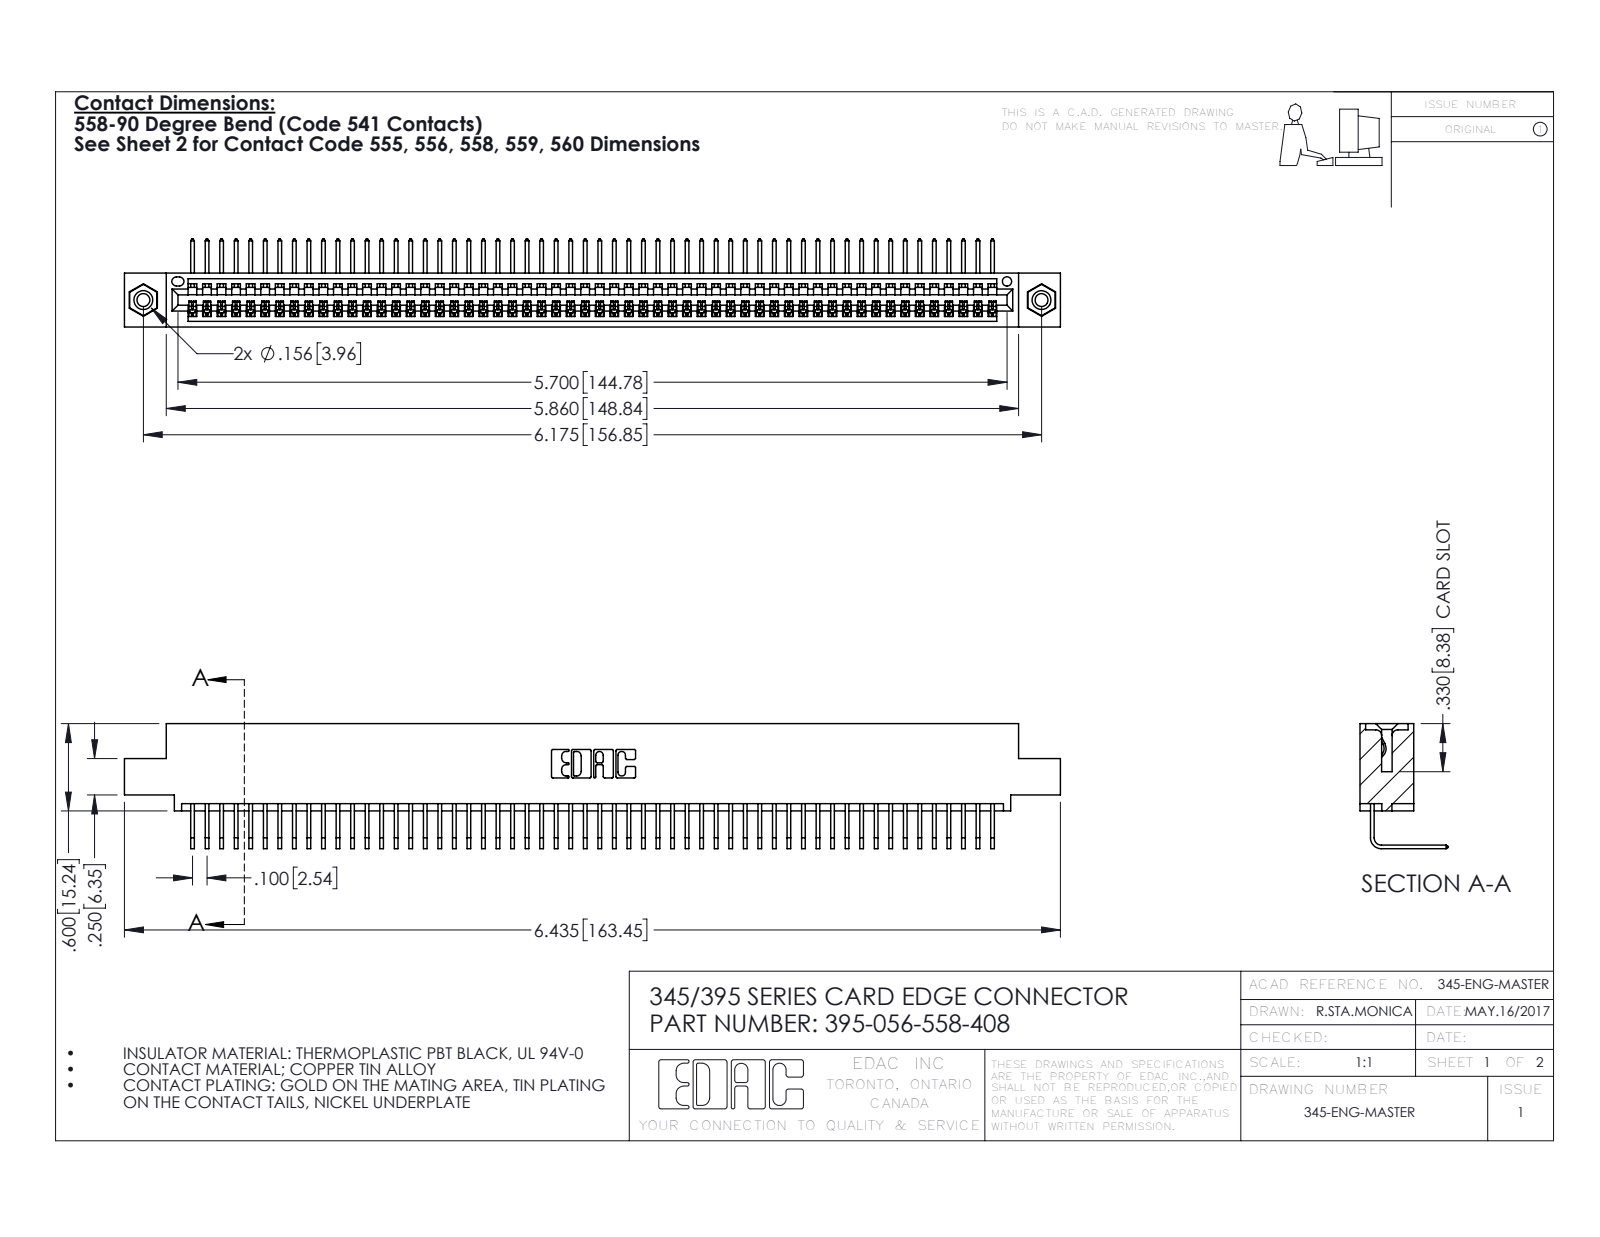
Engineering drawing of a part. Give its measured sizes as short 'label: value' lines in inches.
name: 345-292-001_558 Tail - 2; 345-250-001_345-250-003-102; 395-056-558-408; 345 Part_0.110 Offset - 0.156 Dia-TI
written by: SolidWorks 2016 (CONFIG_CONTROL_DESIGN)
unit: in
bodies: 59 solids, 3550 faces (2468 planar, 1066 cylindrical, 16 other)
size: 6.435 × 0.859 × 0.605
volume: 0.961 in³; area: 34.58 in²
holes: 2× ⌀0.089, 2× ⌀0.125, 2× ⌀0.156, 1× ⌀0.064
bosses: 2× ⌀0.155
rounds: 112× R0.006, 22× R0.01, 6× R0.007, 6× R0.031, 3× R0.026, 2× R0.031, 2× R0.04, 1× R0.014
face distances: 0.072, 0.298, 0.37, 0.2, 0.098, 0.272, 0.025, 0.225, 0.149, 0.072
hole spacings: 0.27, 5.939, 6.175
